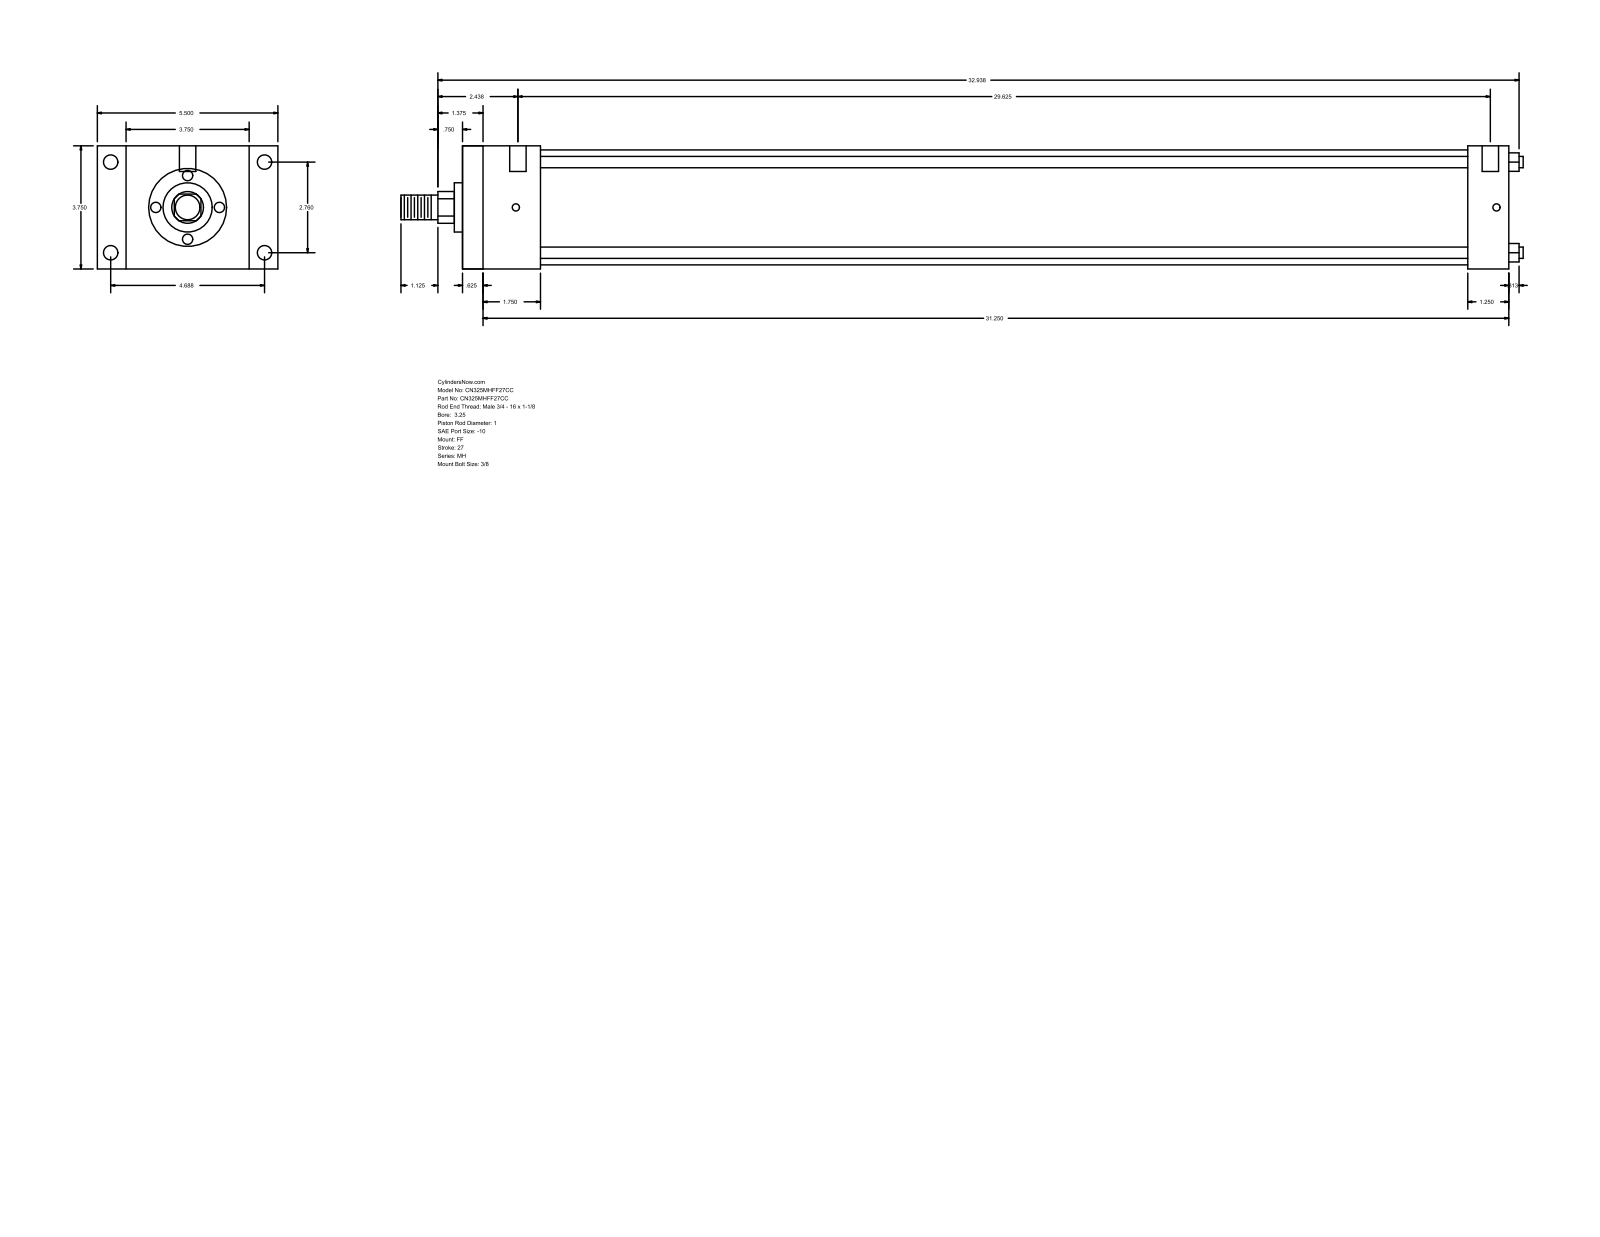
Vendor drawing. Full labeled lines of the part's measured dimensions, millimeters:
Part name (STEP PRODUCT): MH_FF__0325_1
STEP written by: GSSL Pune (CONFIG_CONTROL_DESIGN)
Units: millimetres
Bodies: 0 solids, 92 faces (64 planar, 28 cylindrical, 0 other)
Overall size (bounding box): 868.36 × 139.7 × 95.25
Round holes (diameter × count): ⌀5.56 ×4, ⌀11.13 ×4, ⌀12.7 ×2
Round bosses / shafts (diameter × count): ⌀8.76 ×4, ⌀88.9 ×1, ⌀38.1 ×1, ⌀25.4 ×1, ⌀19.05 ×1
Partial cylindrical surfaces — rounded edges, fillets, slot ends (radius × count): R12.29 ×1
Main face-to-face distances: 95.24, 809.62, 15.87, 793.75, 22.23, 117.47, 777.87, 762, 31.75, 60.33
Hole centre spacings: 70.1, 119.06, 138.16, 758.82, 1.58, 4.76, 752.48, 754.06
